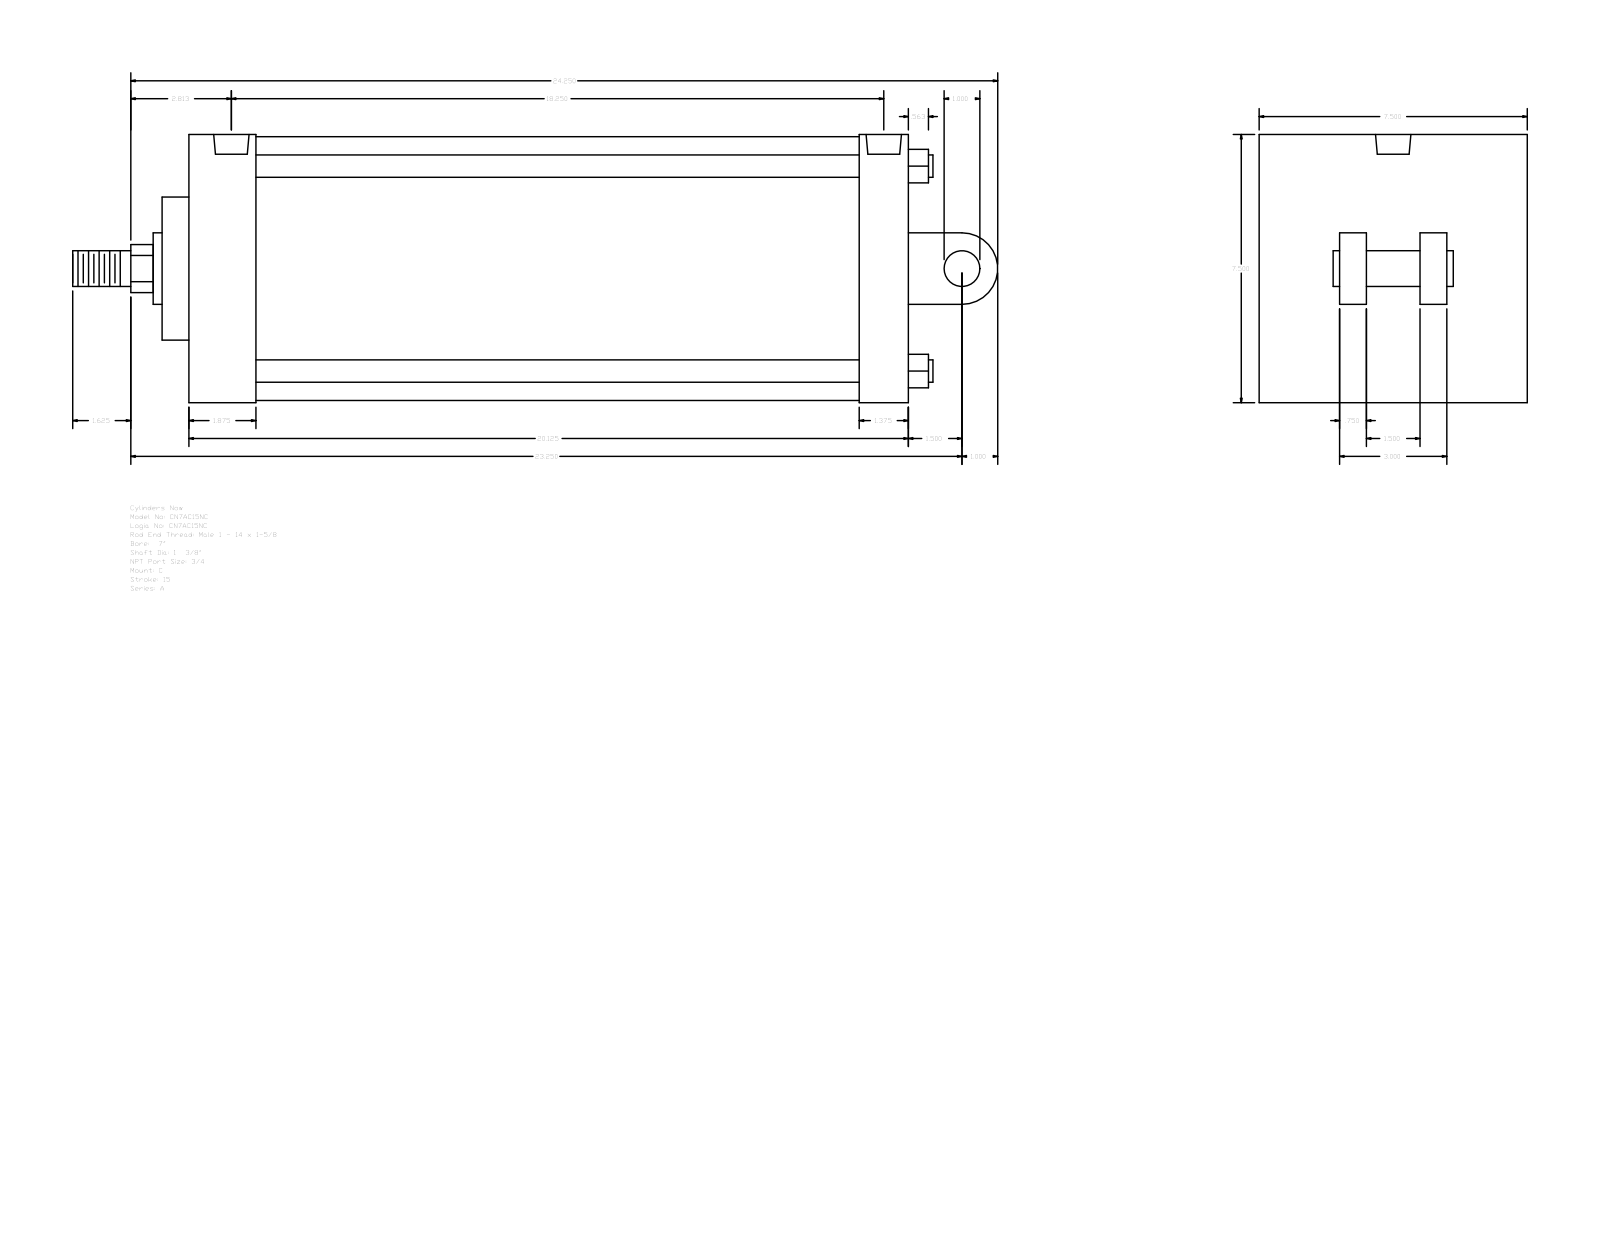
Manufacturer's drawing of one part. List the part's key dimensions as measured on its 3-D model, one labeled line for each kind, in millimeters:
Part name (STEP PRODUCT): A_C__0700_1.375
STEP written by: GSSL Pune (CONFIG_CONTROL_DESIGN)
Units: millimetres
Bodies: 0 solids, 104 faces (75 planar, 29 cylindrical, 0 other)
Overall size (bounding box): 657.23 × 190.5 × 190.5
Round holes (diameter × count): ⌀15.08 ×4, ⌀25.12 ×2
Round bosses / shafts (diameter × count): ⌀15.88 ×4, ⌀25.4 ×2, ⌀187.32 ×1, ⌀50.8 ×1, ⌀34.92 ×1
Partial cylindrical surfaces — rounded edges, fillets, slot ends (radius × count): R17.06 ×1, R25.4 ×1
Main face-to-face distances: 190.5, 511.18, 76.2, 57.15, 19.04, 530.22, 66.67, 47.63, 463.55, 495.29
Hole centre spacings: 5.56, 452.43, 457.99, 463.55
